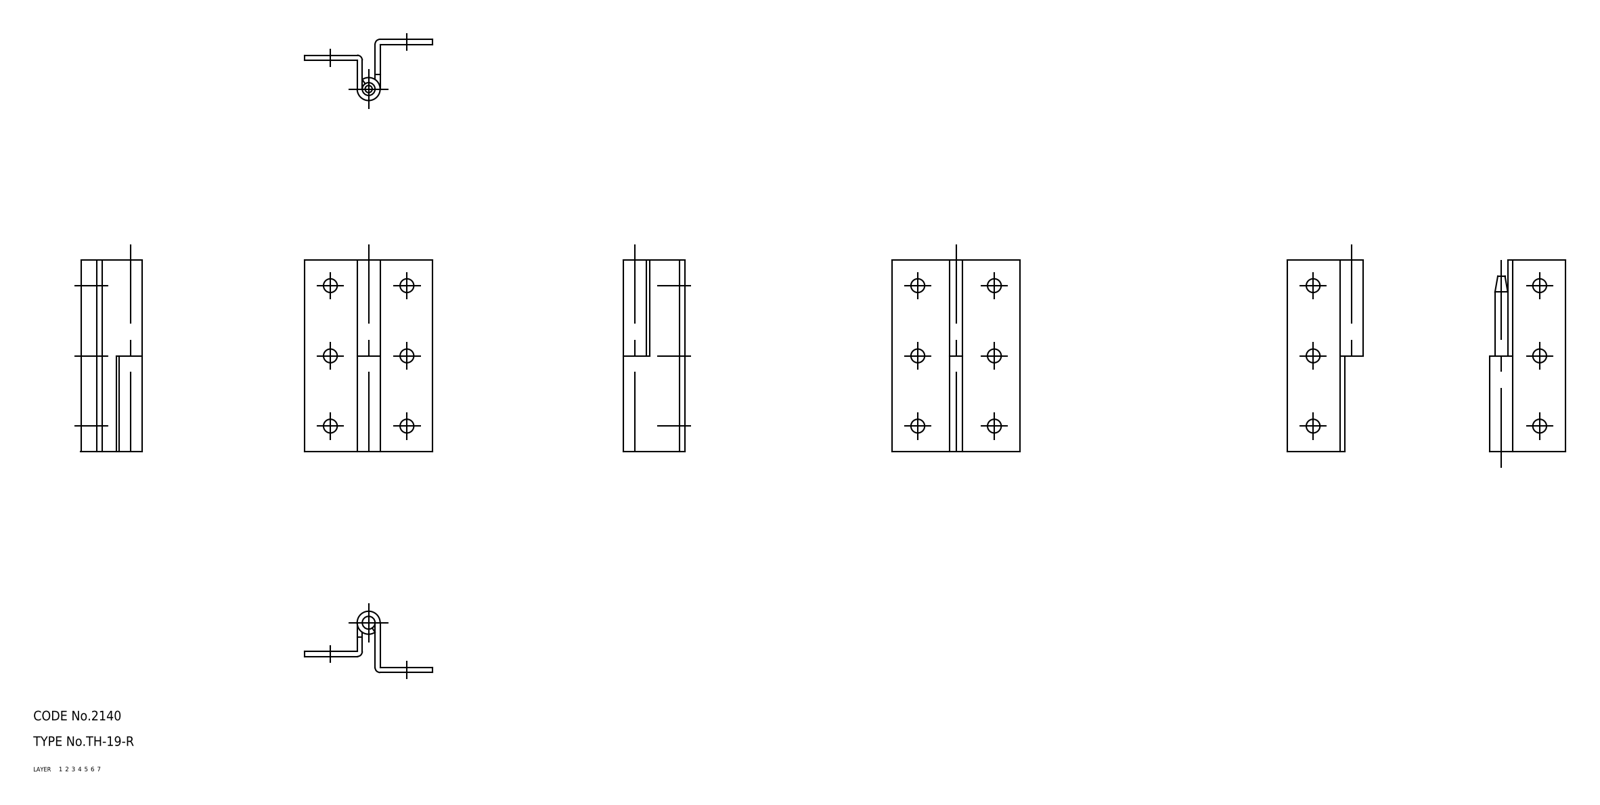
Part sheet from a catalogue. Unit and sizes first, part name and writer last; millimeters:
Units: millimetres
Overall size (bounding box): 60 × 40 × 19.2
Volume: 7 107 mm³ · Surface area: 9 537 mm²
Bodies: 3 solids, 44 faces (0 planar, 0 cylindrical, 44 other)
Part name (STEP PRODUCT): shaft; hinge piece_B; hinge piece_A; TH_19_R_6041_36
STEP written by: CADfix (AUTOMOTIVE_DESIGN)
